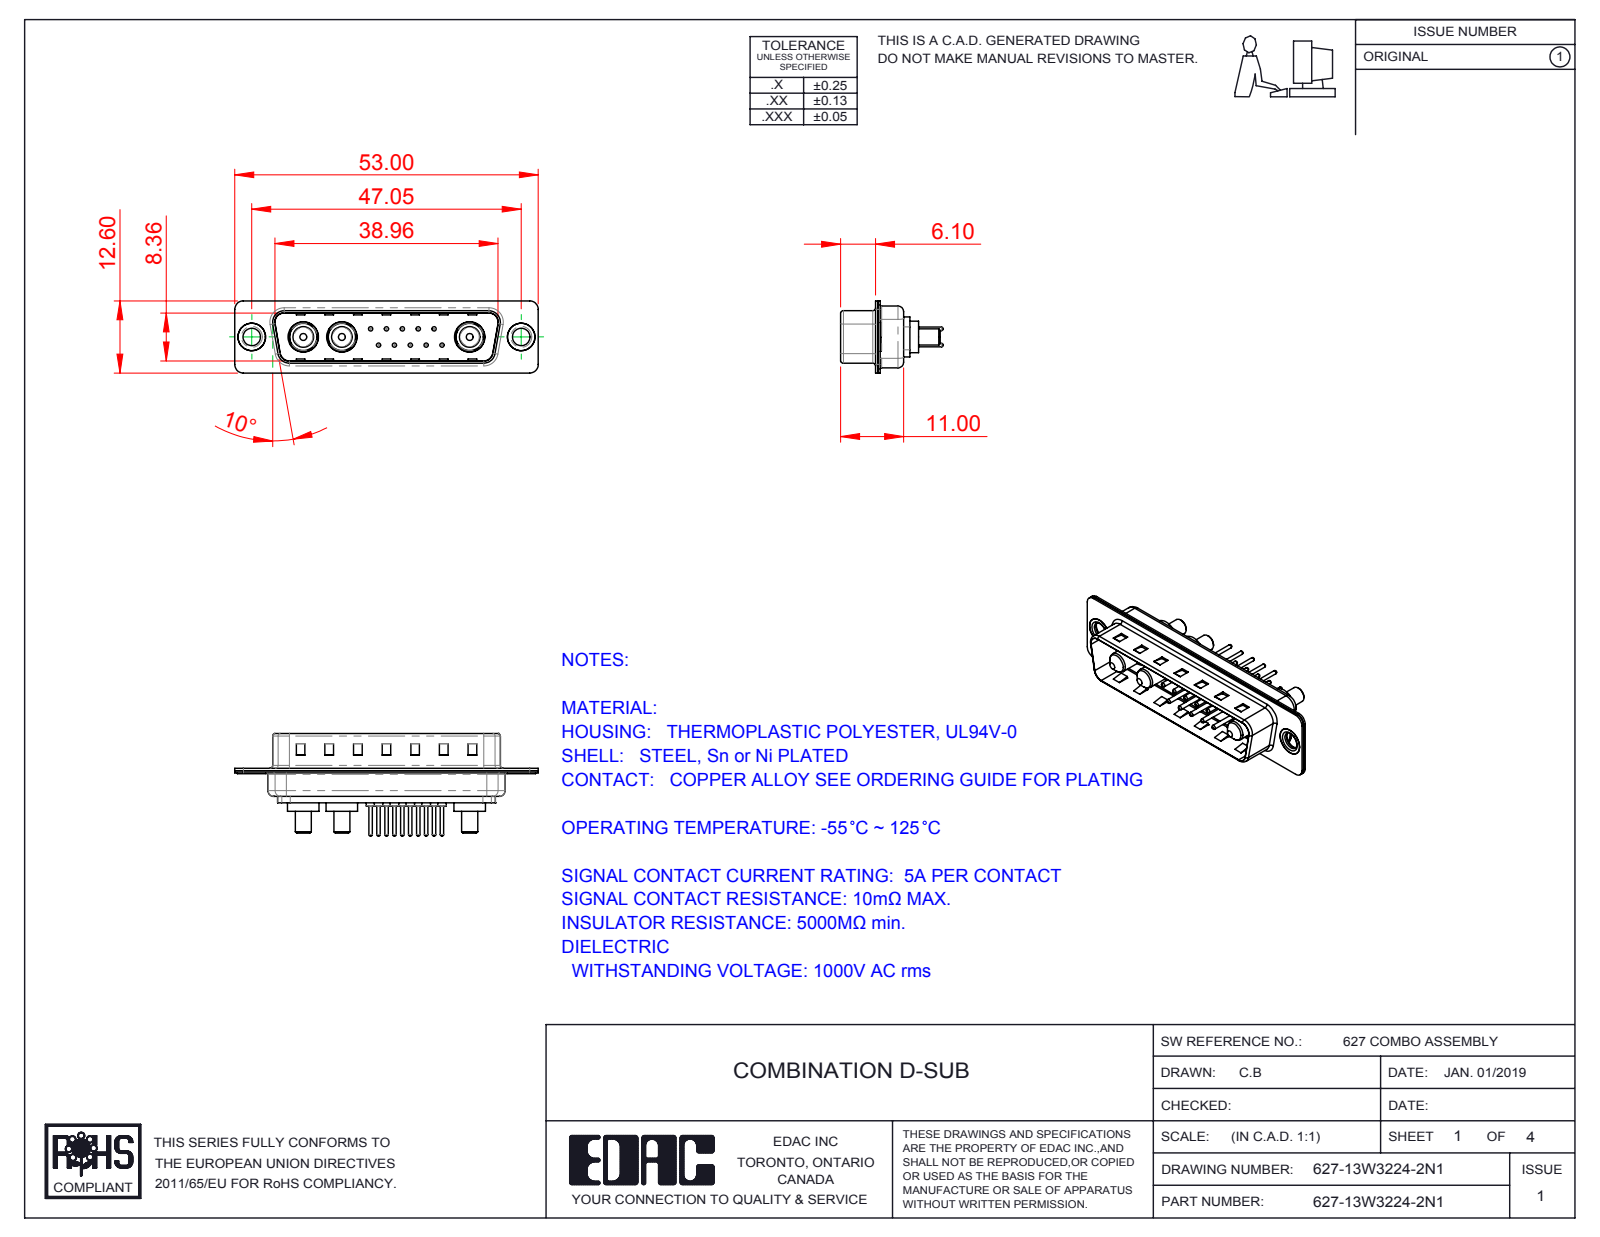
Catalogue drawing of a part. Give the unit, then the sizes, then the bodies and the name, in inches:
Units: inches
Overall size (bounding box): 2.087 × 0.705 × 0.496
Round holes (diameter × count): ⌀0.03 ×10, ⌀0.063 ×10, ⌀0.079 ×10, ⌀0.191 ×3, ⌀0.209 ×3, ⌀0.12 ×2, ⌀0.157 ×2, ⌀0.189 ×2
Round bosses / shafts (diameter × count): ⌀0.059 ×10, ⌀0.024 ×10, ⌀0.217 ×3, ⌀0.205 ×3, ⌀0.187 ×3, ⌀0.148 ×3, ⌀0.142 ×3, ⌀0.11 ×3
Partial cylindrical surfaces — rounded edges, fillets, slot ends (radius × count): R0.059 ×16, R0.079 ×12, R0.02 ×8, R0.063 ×8, R0.01 ×4, R0.024 ×4, R0.026 ×4, R0.035 ×4
Main face-to-face distances: 0.016, 0.032, 0.377, 0.345, 0.059, 0.22, 0.031, 0.205, 0.048, 0.393
Hole centre spacings: 0.124, 0.109, 0.198, 0.218, 0.295, 0.198, 0.327, 0.398
Volume: 0.174 in³ · Surface area: 10.24 in²
Bodies: 21 solids, 840 faces (271 planar, 318 cylindrical, 251 other)
Part name (STEP PRODUCT): 627Combo Housing_13W3; 627-13W3224-2N1; Power Pin_20A S; 627Combo Shell Rear_25 Contacts (+4 more)
STEP written by: SolidWorks 2016 (CONFIG_CONTROL_DESIGN)
